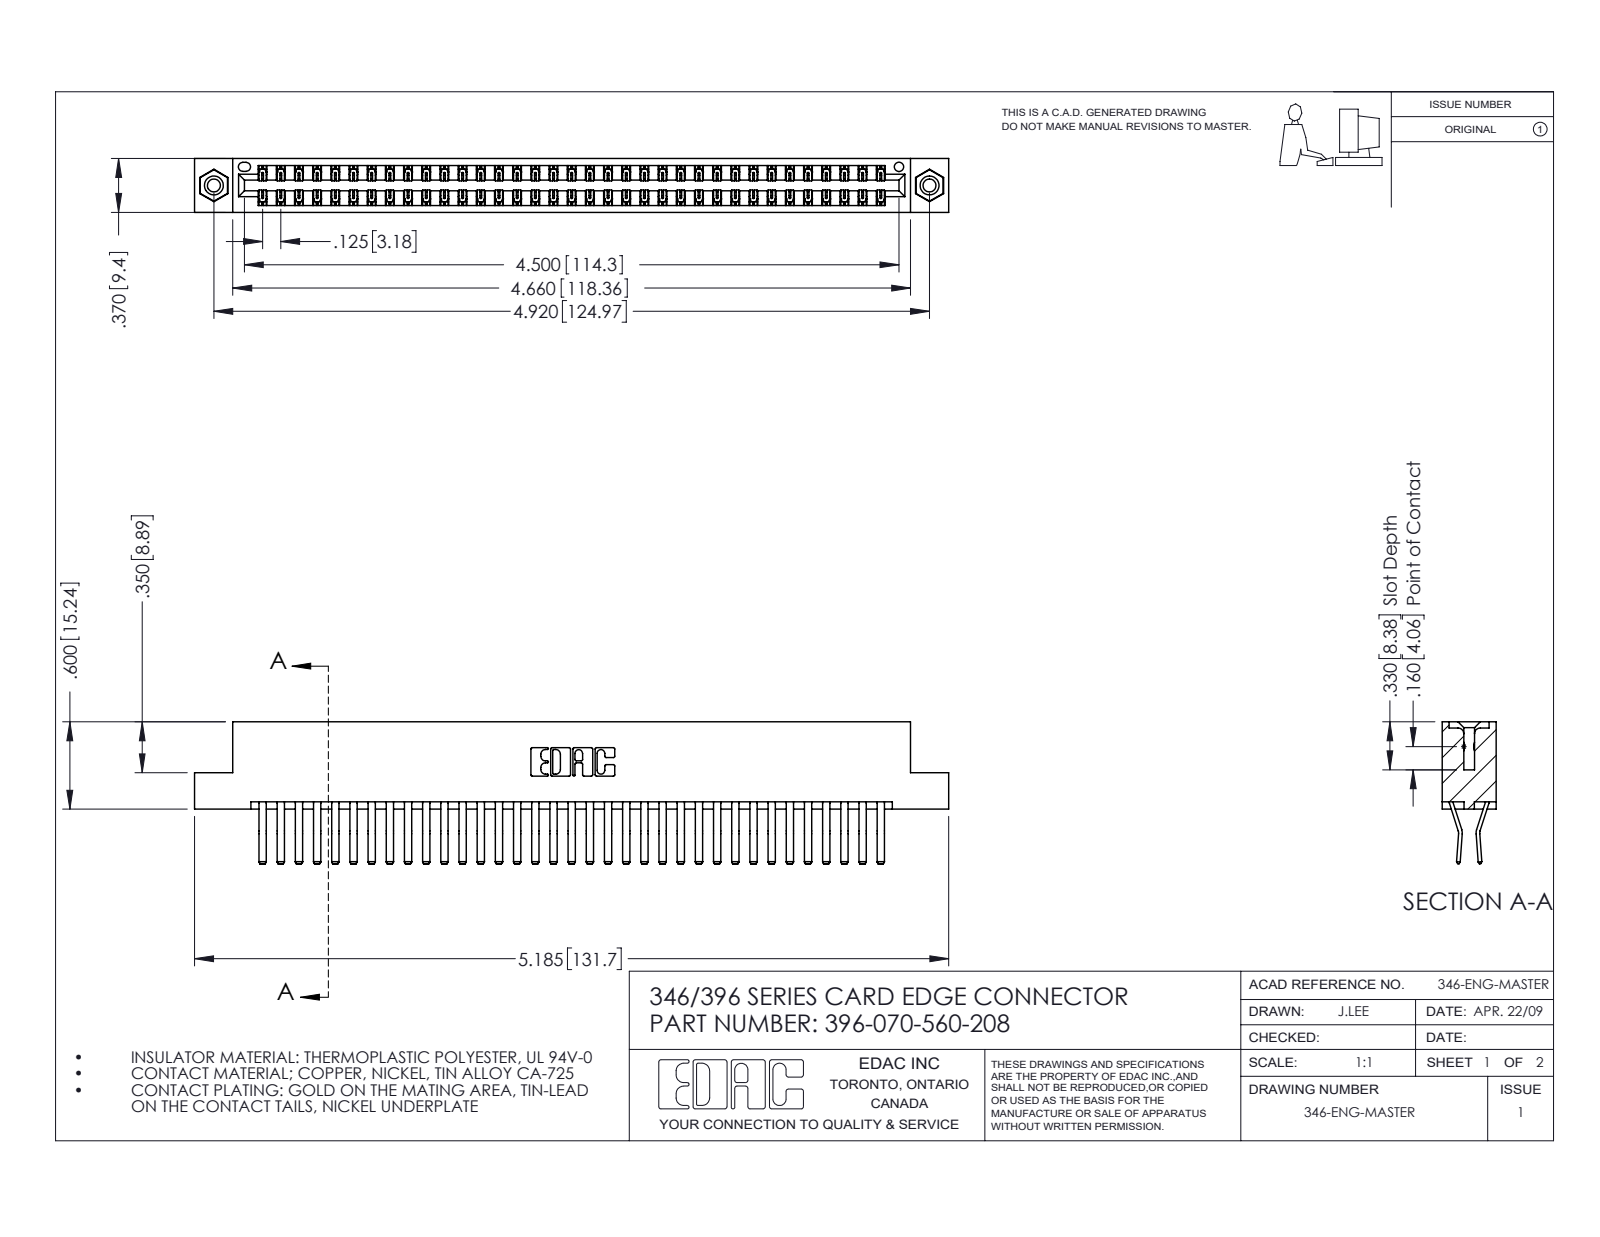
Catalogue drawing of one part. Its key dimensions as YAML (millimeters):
part_name: "396-070-560-208; 345-292-001_560 Tail; 345-250-001_345-250-003-102; 346 Part_Flush Mounting Lugs - 0.156 Dia-TI"
step_written_by: "SolidWorks 2016 (CONFIG_CONTROL_DESIGN)"
units: millimeters
bodies: {solids: 73, faces: 3962, planar: 2558, cylindrical: 1388, other: 16}
overall_size: [131.7, 24.8, 9.4]
volume: 13200
surface_area: 19340
round_holes:
  - {diameter: 2.3, count: 2}
  - {diameter: 3.2, count: 2}
  - {diameter: 4, count: 2}
  - {diameter: 1.6, count: 1}
round_bosses_or_shafts:
  - {diameter: 3.9, count: 2}
partial_cylinders:
  - {radius: 0.2, count: 105}
  - {radius: 0.3, count: 22}
  - {radius: 0.2, count: 6}
  - {radius: 0.8, count: 6}
  - {radius: 0.7, count: 3}
  - {radius: 0.3, count: 2}
  - {radius: 0.4, count: 2}
  - {radius: 0.6, count: 2}
face_to_face_distances: [1.2, 8.2, 9.4, 0.6, 6.4, 1.8, 7.6, 7, 3.8, 5.6]
hole_center_spacings: [6.2, 119.7, 125]
